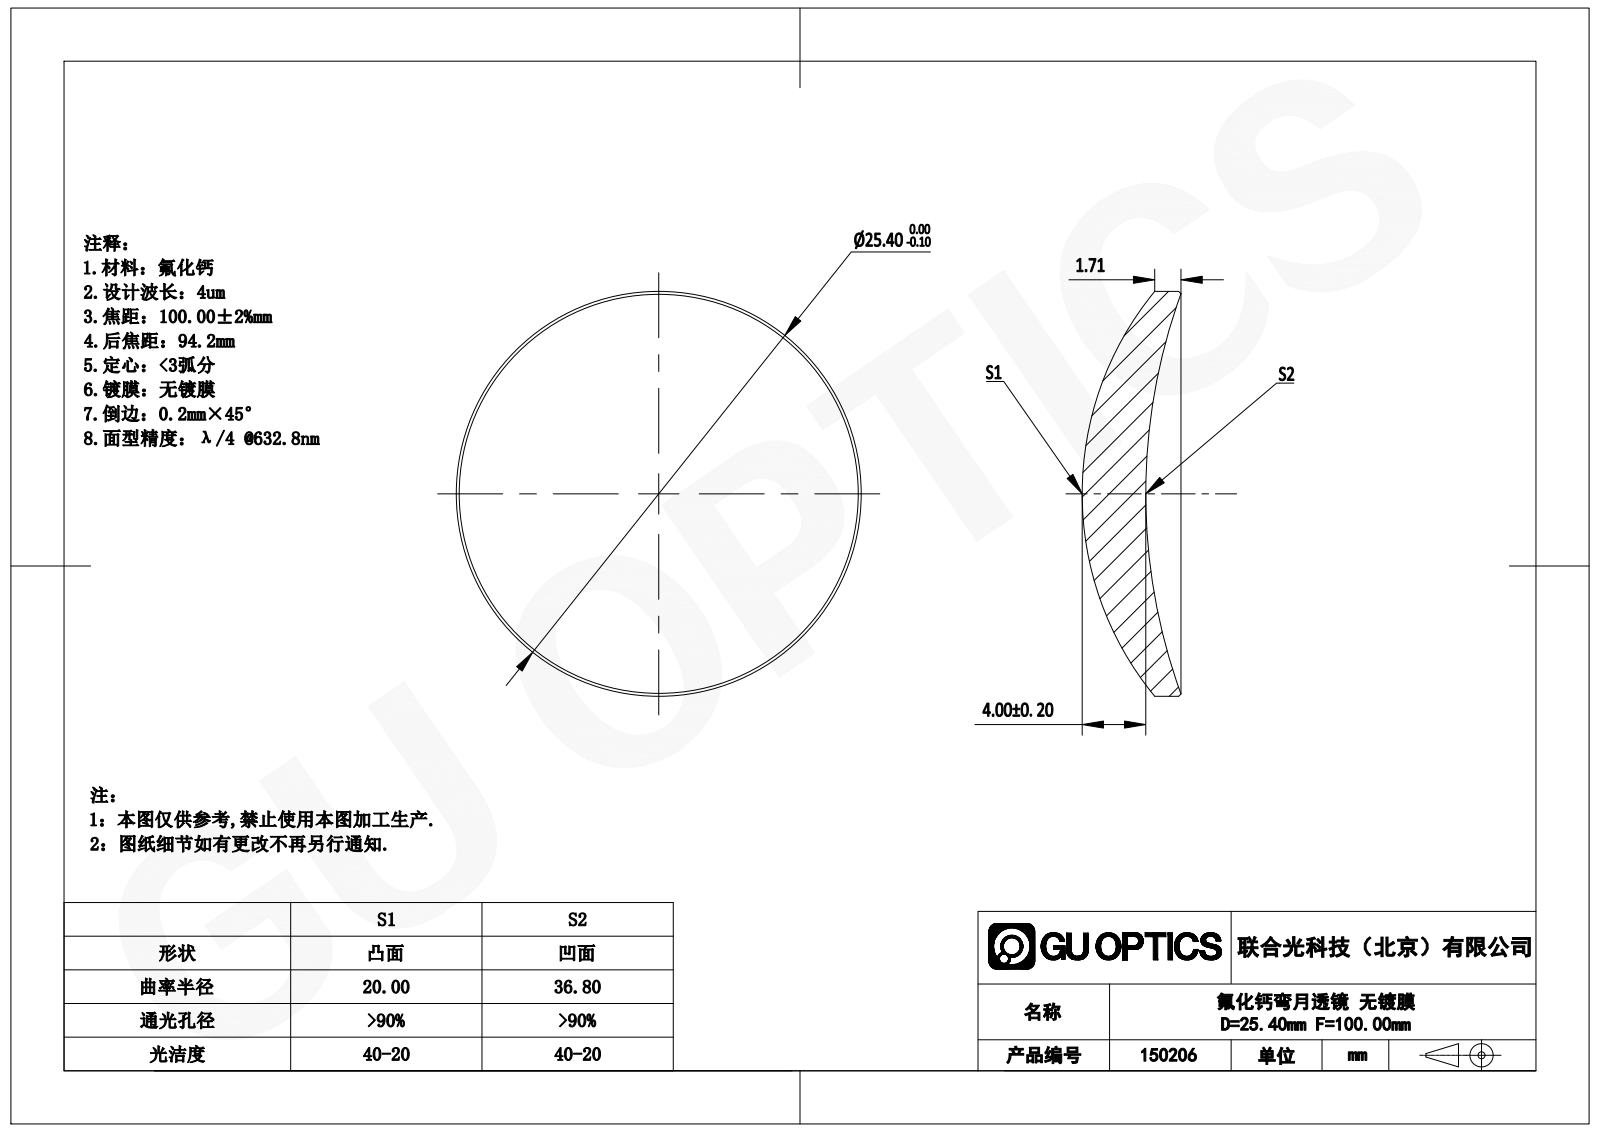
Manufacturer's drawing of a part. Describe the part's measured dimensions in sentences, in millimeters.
The part is named "GLM5-025B-100". Its 3-D file was written by "SolidWorks 2022 (AUTOMOTIVE_DESIGN)". It is 1 solid with 8 faces: 0 planar, 2 cylindrical and 6 other. Overall it measures 25.4 by 25.4 by 6.2 millimeters. Its volume is 1 483 cubic millimeters and its surface area 1 218 square millimeters. Round bosses or shafts: 1 of diameter 25.4.
